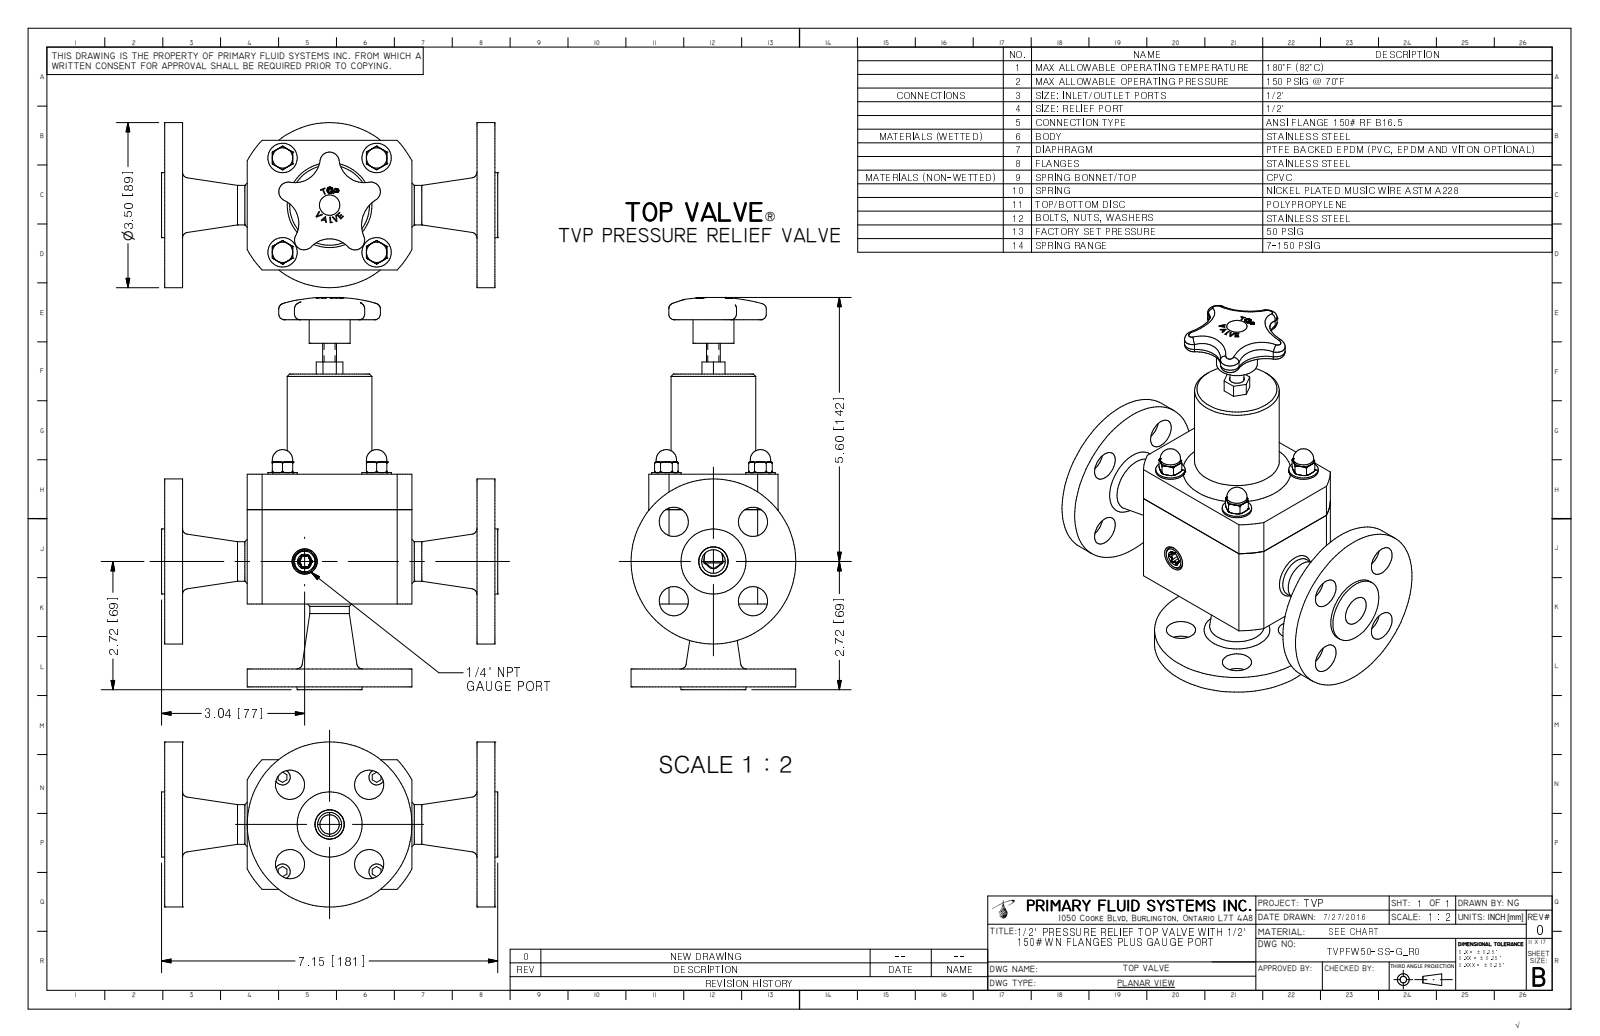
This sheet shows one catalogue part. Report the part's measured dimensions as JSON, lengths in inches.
{"part_name": "TVPFW50-SS-G_R0", "step_written_by": "Autodesk Inventor 2009 (AUTOMOTIVE_DESIGN)", "units": "inches", "bodies": {"solids": 1, "faces": 374, "planar": 140, "cylindrical": 71, "other": 163}, "overall_size": [8.319, 7.145, 3.5], "volume_in3": 44.21, "surface_area_in2": 168.3, "round_holes": [[0.62, 8], [0.175, 4], [0.622, 2], [2.4, 1]], "round_bosses_or_shafts": [[0.625, 4], [0.433, 4], [3.5, 2], [1.38, 2], [0.84, 2], [2.375, 1], [1.8, 1], [0.87, 1]], "partial_cylinders_radius": [[0.027, 6], [0.085, 5], [0.205, 5], [0.536, 4], [0.656, 4], [0.625, 1], [0.745, 1], [1.988, 1]], "face_to_face_distances": [0.38, 6.64, 2.75, 7.02, 1.757, 6.26, 1.377, 5.263, 4.883, 1.378], "hole_center_spacings": [1.19, 1.683, 1.848, 0.224, 1.414, 2, 2.38, 2.604]}
